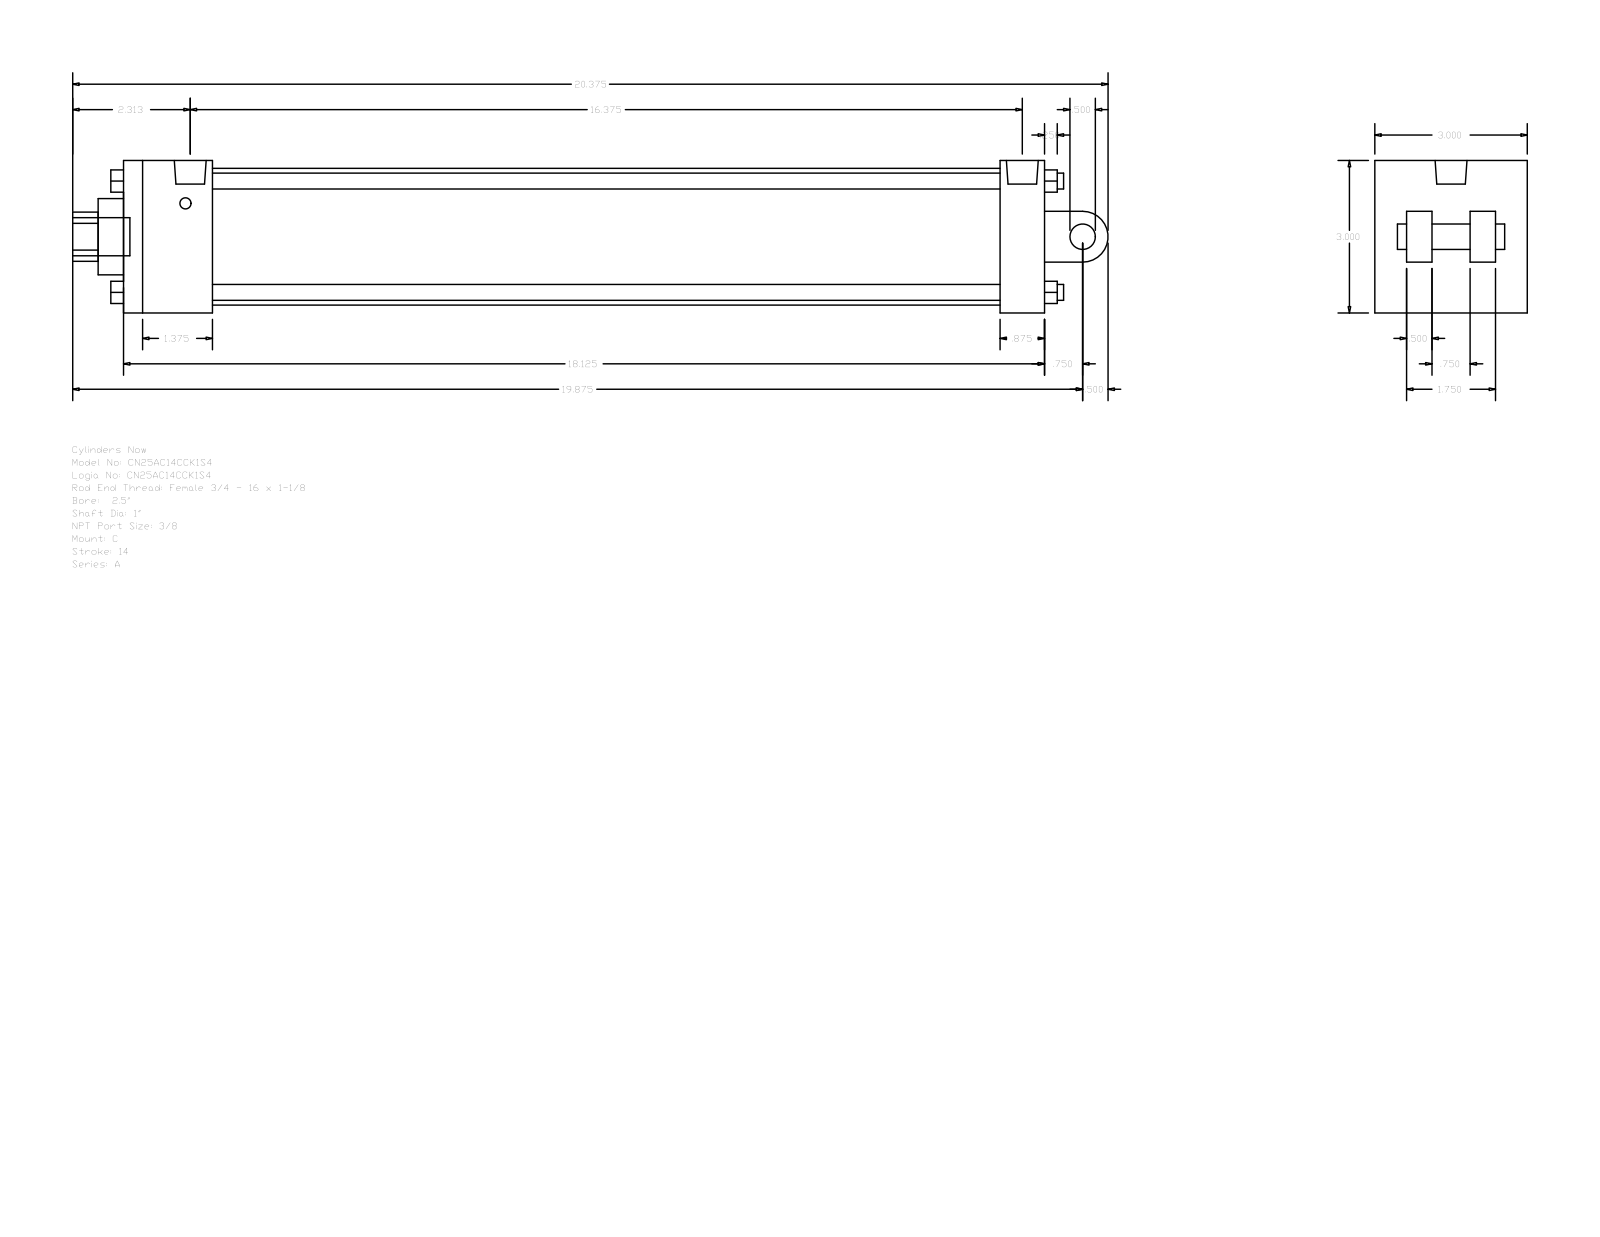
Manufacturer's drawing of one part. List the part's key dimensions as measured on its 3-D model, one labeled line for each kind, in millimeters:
Part name (STEP PRODUCT): A_C__0250_1
STEP written by: GSSL Pune (CONFIG_CONTROL_DESIGN)
Units: millimetres
Bodies: 0 solids, 135 faces (102 planar, 33 cylindrical, 0 other)
Overall size (bounding box): 517.52 × 76.2 × 76.2
Round holes (diameter × count): ⌀5.56 ×2, ⌀15.93 ×1, ⌀25.4 ×1, ⌀38.1 ×1, ⌀68.33 ×1
Round bosses / shafts (diameter × count): ⌀7.94 ×4, ⌀5.56 ×2, ⌀19.05 ×1, ⌀15.93 ×1, ⌀12.7 ×1
Partial cylindrical surfaces — rounded edges, fillets, slot ends (radius × count): R12.29 ×1, R12.7 ×1
Main face-to-face distances: 76.2, 460.37, 12.7, 44.45, 438.15, 393.7, 415.92, 22.22, 15.87, 25.4
Hole centre spacings: 2.38
